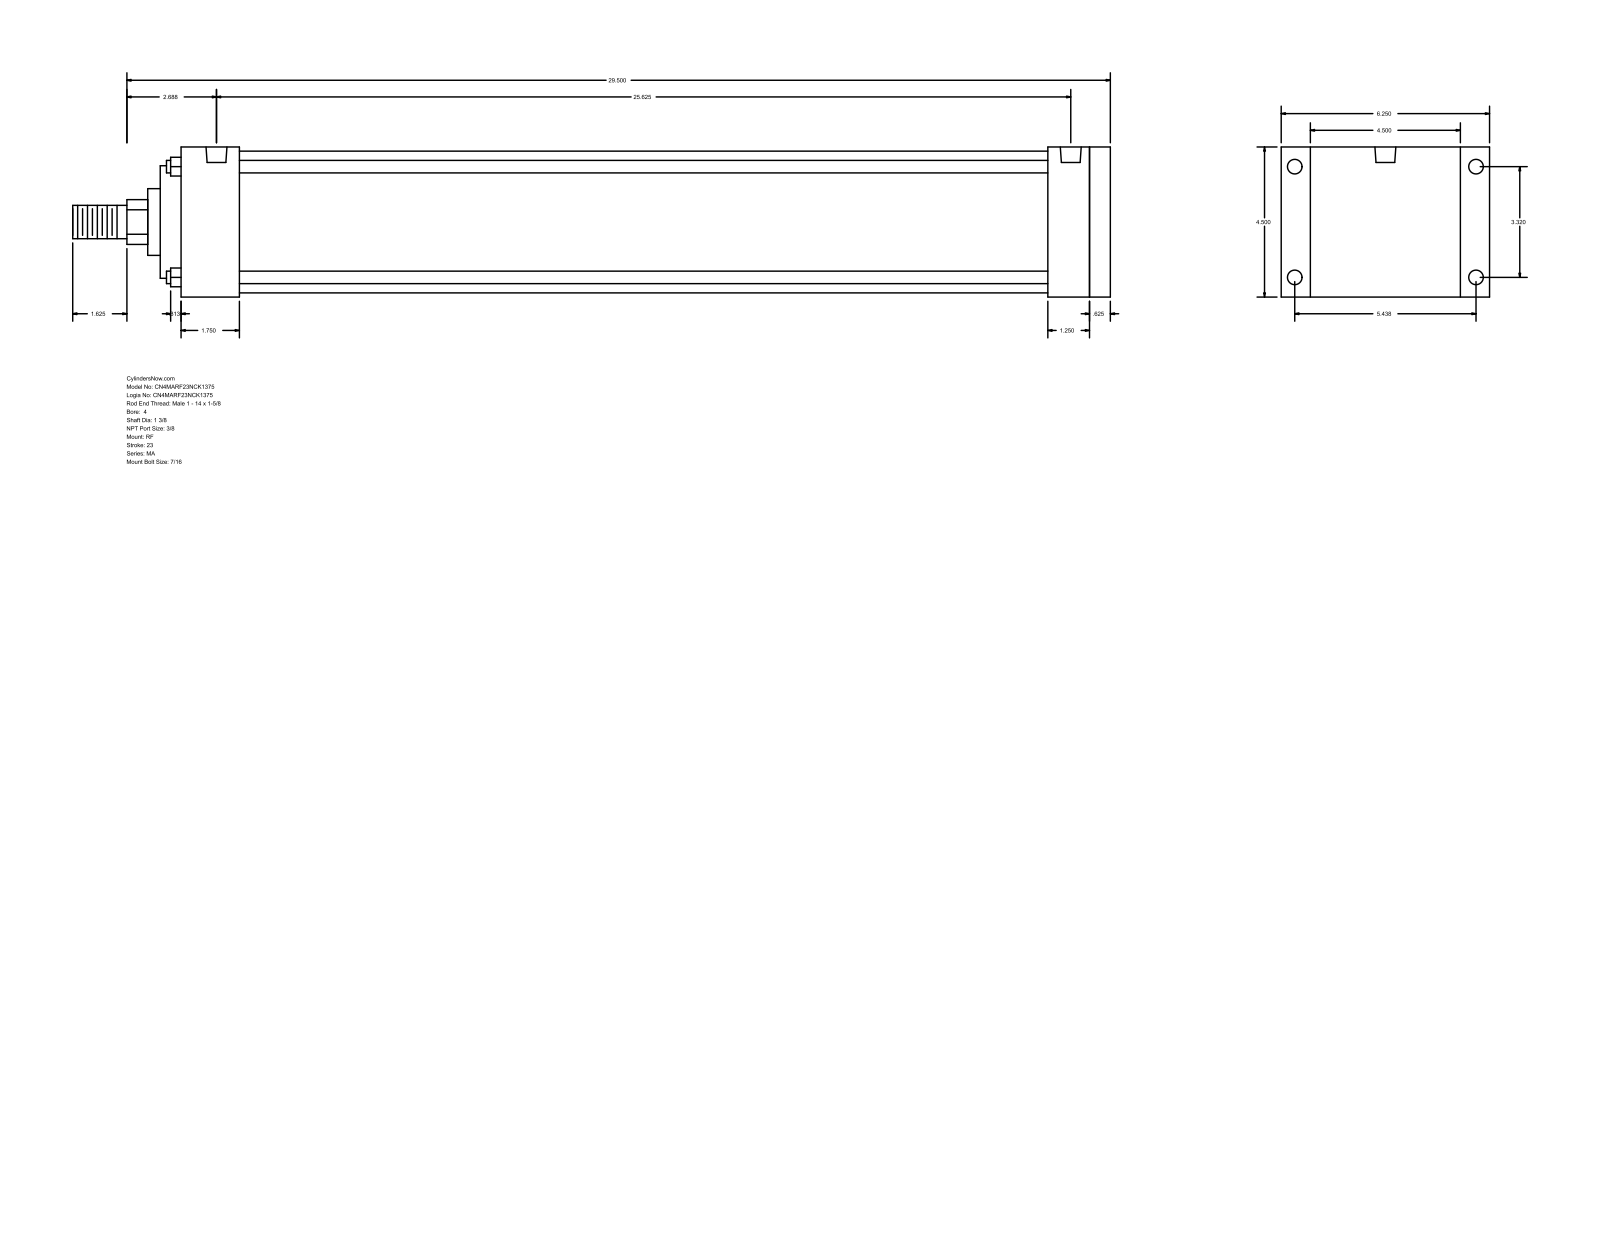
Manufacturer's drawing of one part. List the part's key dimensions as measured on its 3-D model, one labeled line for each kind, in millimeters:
Part name (STEP PRODUCT): MA_RF__0400_1.375
STEP written by: GSSL Pune (CONFIG_CONTROL_DESIGN)
Units: millimetres
Bodies: 0 solids, 94 faces (65 planar, 29 cylindrical, 0 other)
Overall size (bounding box): 790.58 × 158.75 × 114.3
Round holes (diameter × count): ⌀11.11 ×8, ⌀15.93 ×2
Round bosses / shafts (diameter × count): ⌀9.53 ×4, ⌀107.95 ×1, ⌀85.72 ×1, ⌀50.8 ×1, ⌀34.92 ×1, ⌀25.4 ×1
Partial cylindrical surfaces — rounded edges, fillets, slot ends (radius × count): R17.06 ×1
Main face-to-face distances: 114.3, 708.03, 15.88, 692.15, 15.87, 708.02, 723.9, 22.23, 136.53, 676.27
Hole centre spacings: 84.32, 138.12, 161.82, 641.35, 4.76, 4.77, 646.11, 646.12
